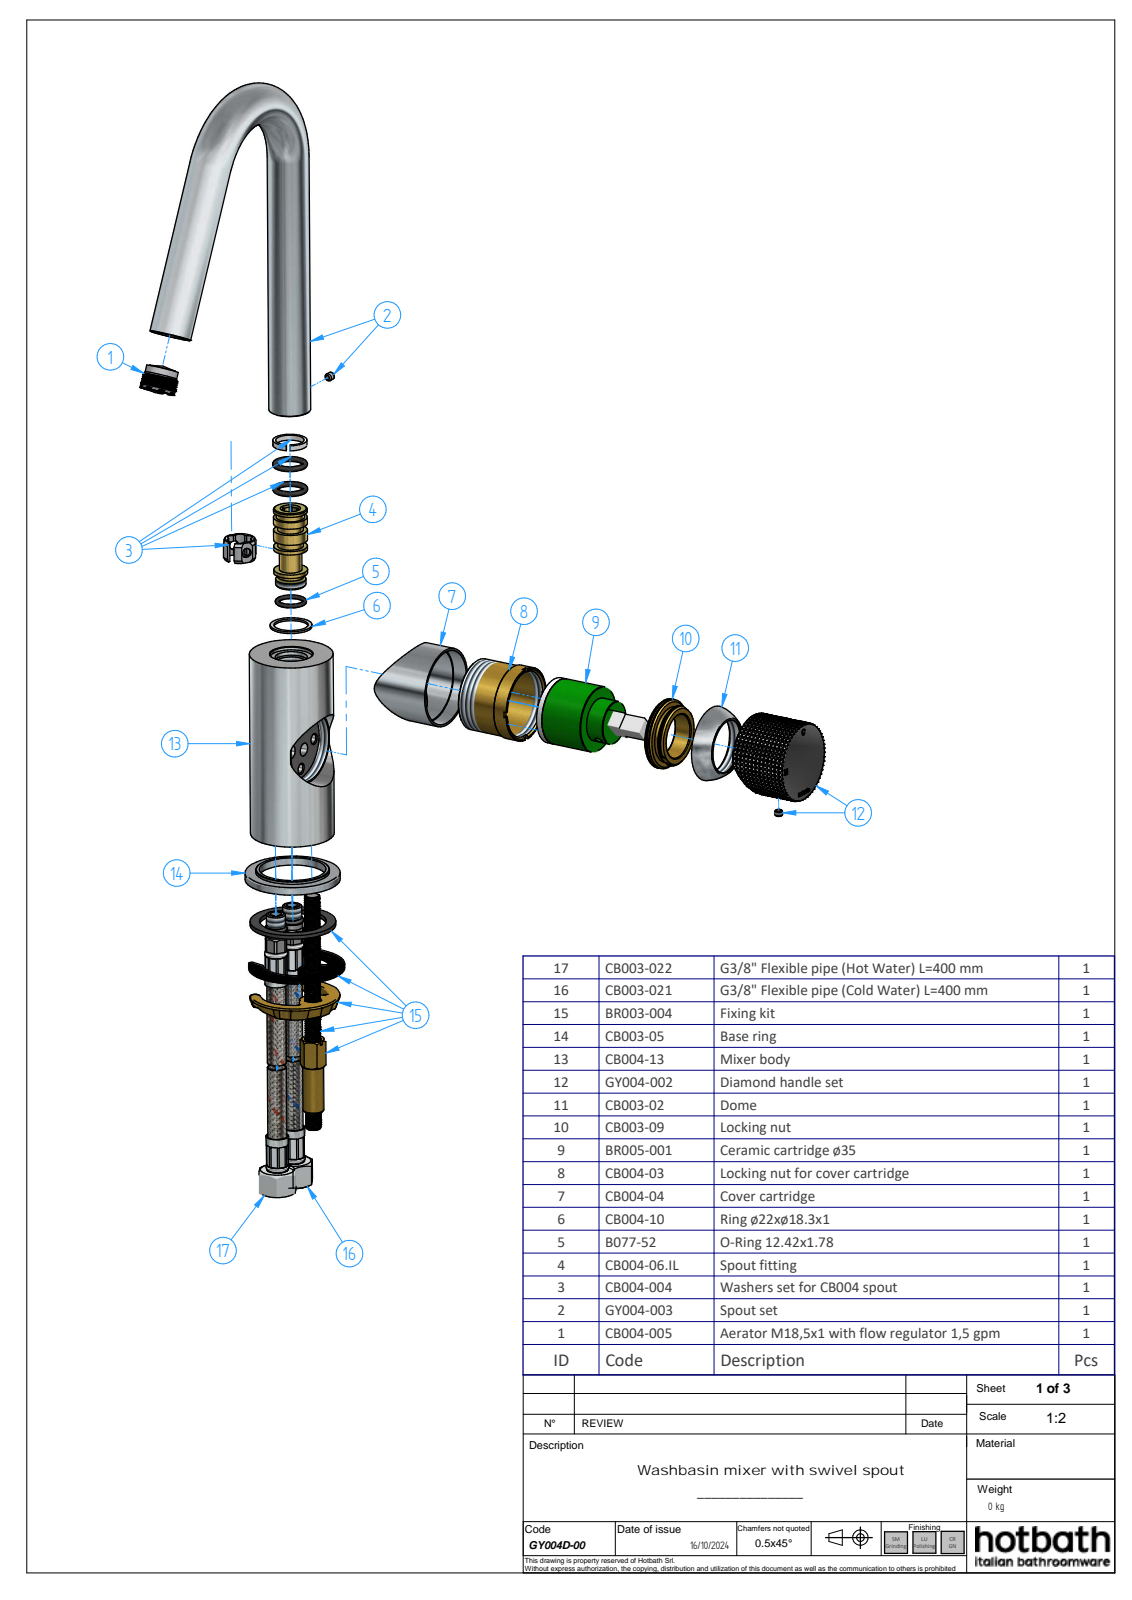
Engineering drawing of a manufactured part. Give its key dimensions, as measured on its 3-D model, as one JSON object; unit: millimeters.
{"part_name": "GY004D-00; GY004-003; GY004-03; CB004-11 (+7 more)", "step_written_by": "Solid Edge (AUTOMOTIVE_DESIGN)", "units": "millimeters", "bodies": {"solids": 8, "faces": 5239, "planar": 1957, "cylindrical": 2874, "other": 408}, "overall_size": [295.41, 150.71, 95.55], "volume_mm3": 162692, "surface_area_mm2": 95144, "round_holes": [[0.75, 116], [5, 3], [7, 3], [11, 3], [6, 2], [8.92, 2], [18, 2], [3.24, 1], [4.2, 1], [6.65, 1], [8, 1], [13.8, 1]], "round_bosses_or_shafts": [[22, 2], [50, 1], [42, 1], [38.7, 1], [18.5, 1], [18.4, 1], [18, 1], [17.42, 1]], "partial_cylinders_radius": [[0.1, 59], [0.49, 1], [6.5, 1]], "face_to_face_distances": [100, 18, 82, 62.8, 2.5, 20.5, 102.5, 4, 1.5, 75.5], "hole_center_spacings": [3.07, 3.18, 5.35, 5.49, 6.26, 1.02, 1.2, 3.08]}
